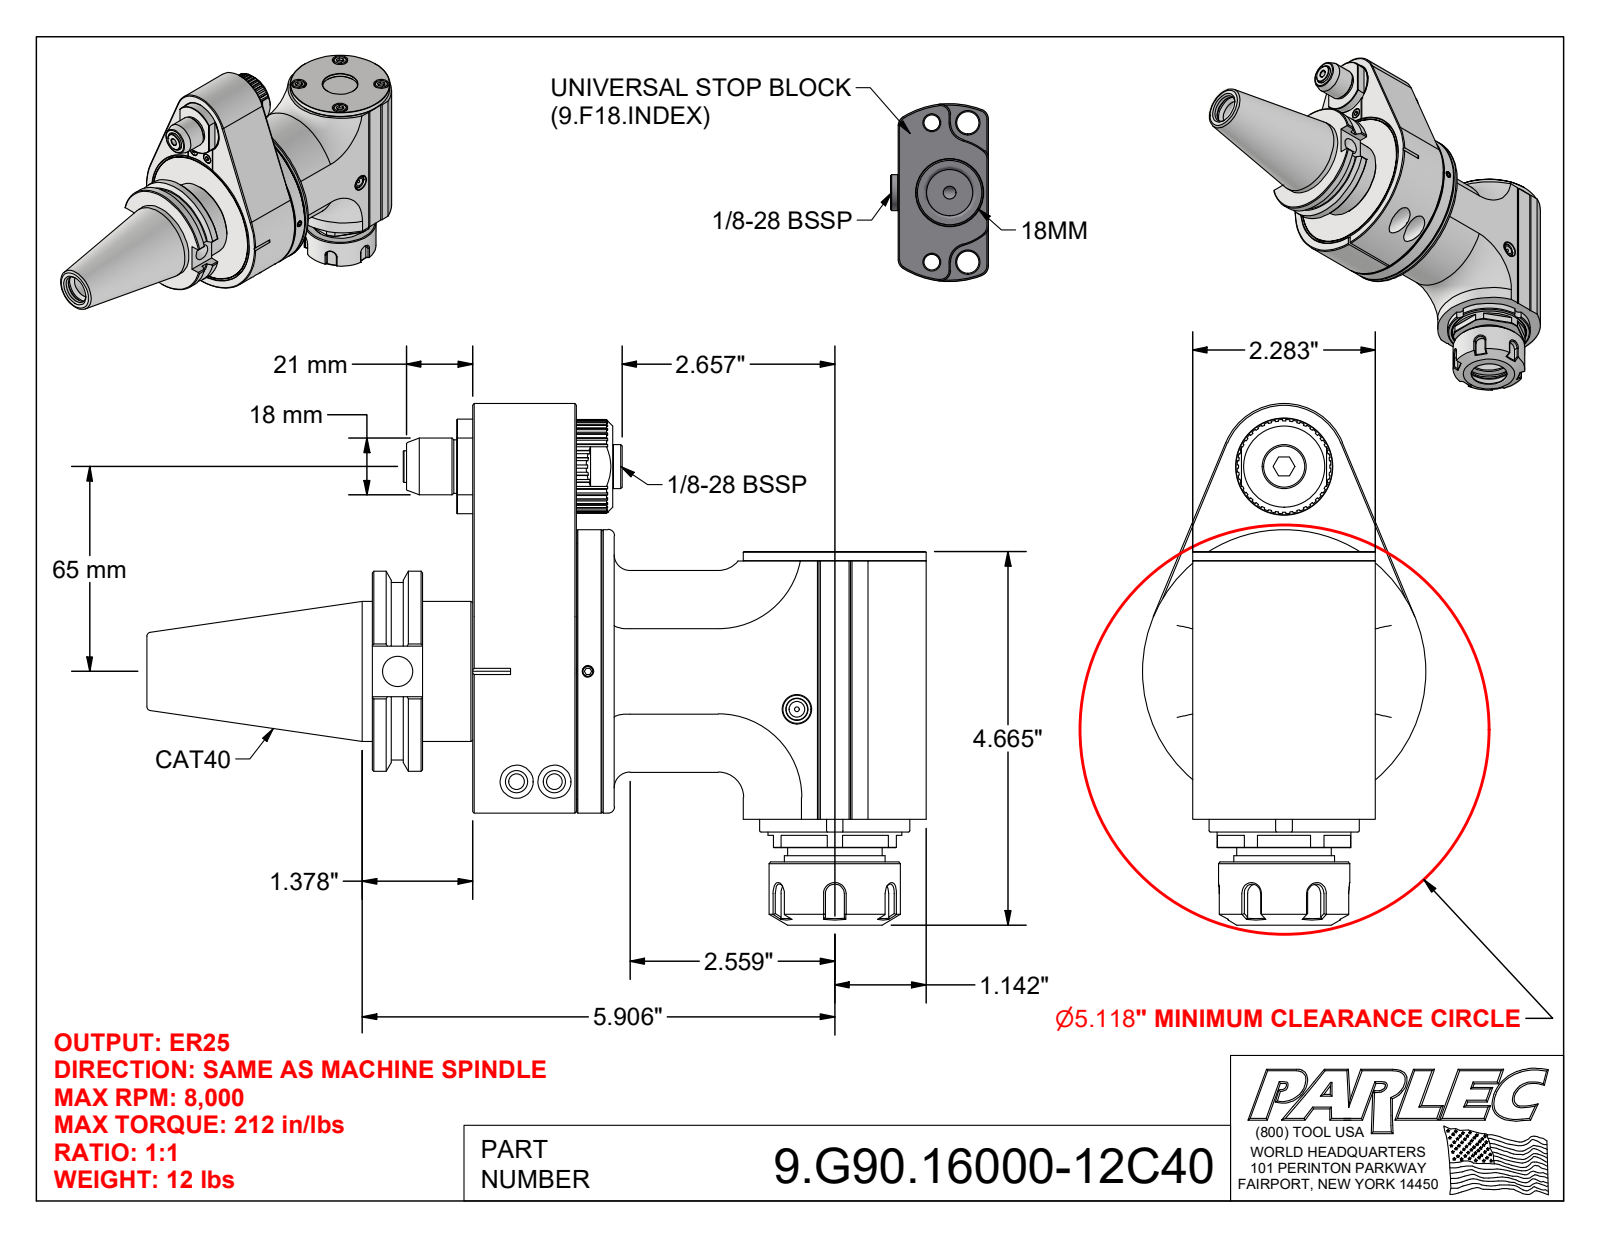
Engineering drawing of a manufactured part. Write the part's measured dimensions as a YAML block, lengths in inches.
part_name: "9.G90.16000-12C40; 9_GA1_446_1 (Classic, Type 1, Cat40, 65mm); 9_G90_16000"
step_written_by: "Autodesk Inventor 2022 (AUTOMOTIVE_DESIGN)"
units: inches
bodies: {solids: 5, faces: 1080, planar: 694, cylindrical: 165, other: 221}
overall_size: [9.74, 6.516, 3.543]
volume: 52.61
surface_area: 206.1
round_holes:
  - {diameter: 0.165, count: 6}
  - {diameter: 0.197, count: 4}
  - {diameter: 0.157, count: 2}
  - {diameter: 0.236, count: 2}
  - {diameter: 0.276, count: 2}
  - {diameter: 0.413, count: 2}
  - {diameter: 0.551, count: 2}
  - {diameter: 0.709, count: 2}
  - {diameter: 0.13, count: 1}
  - {diameter: 0.335, count: 1}
  - {diameter: 0.354, count: 1}
  - {diameter: 0.433, count: 1}
round_bosses_or_shafts:
  - {diameter: 1.181, count: 2}
  - {diameter: 3.543, count: 1}
  - {diameter: 3.071, count: 1}
  - {diameter: 2.5, count: 1}
  - {diameter: 2.283, count: 1}
  - {diameter: 2.219, count: 1}
  - {diameter: 1.89, count: 1}
  - {diameter: 1.75, count: 1}
partial_cylinders:
  - {radius: 0.118, count: 8}
  - {radius: 1.26, count: 3}
  - {radius: 0.085, count: 2}
  - {radius: 0.197, count: 2}
  - {radius: 0.079, count: 1}
  - {radius: 0.092, count: 1}
  - {radius: 0.098, count: 1}
  - {radius: 0.121, count: 1}
face_to_face_distances: [1.299, 0.315, 0.984, 0.118, 0.197, 1.181, 0.626, 0.472, 2.283, 0.039]
hole_center_spacings: [1.476, 2.557, 0.764, 1.476, 2.088, 2.953, 0.366, 0.817]
